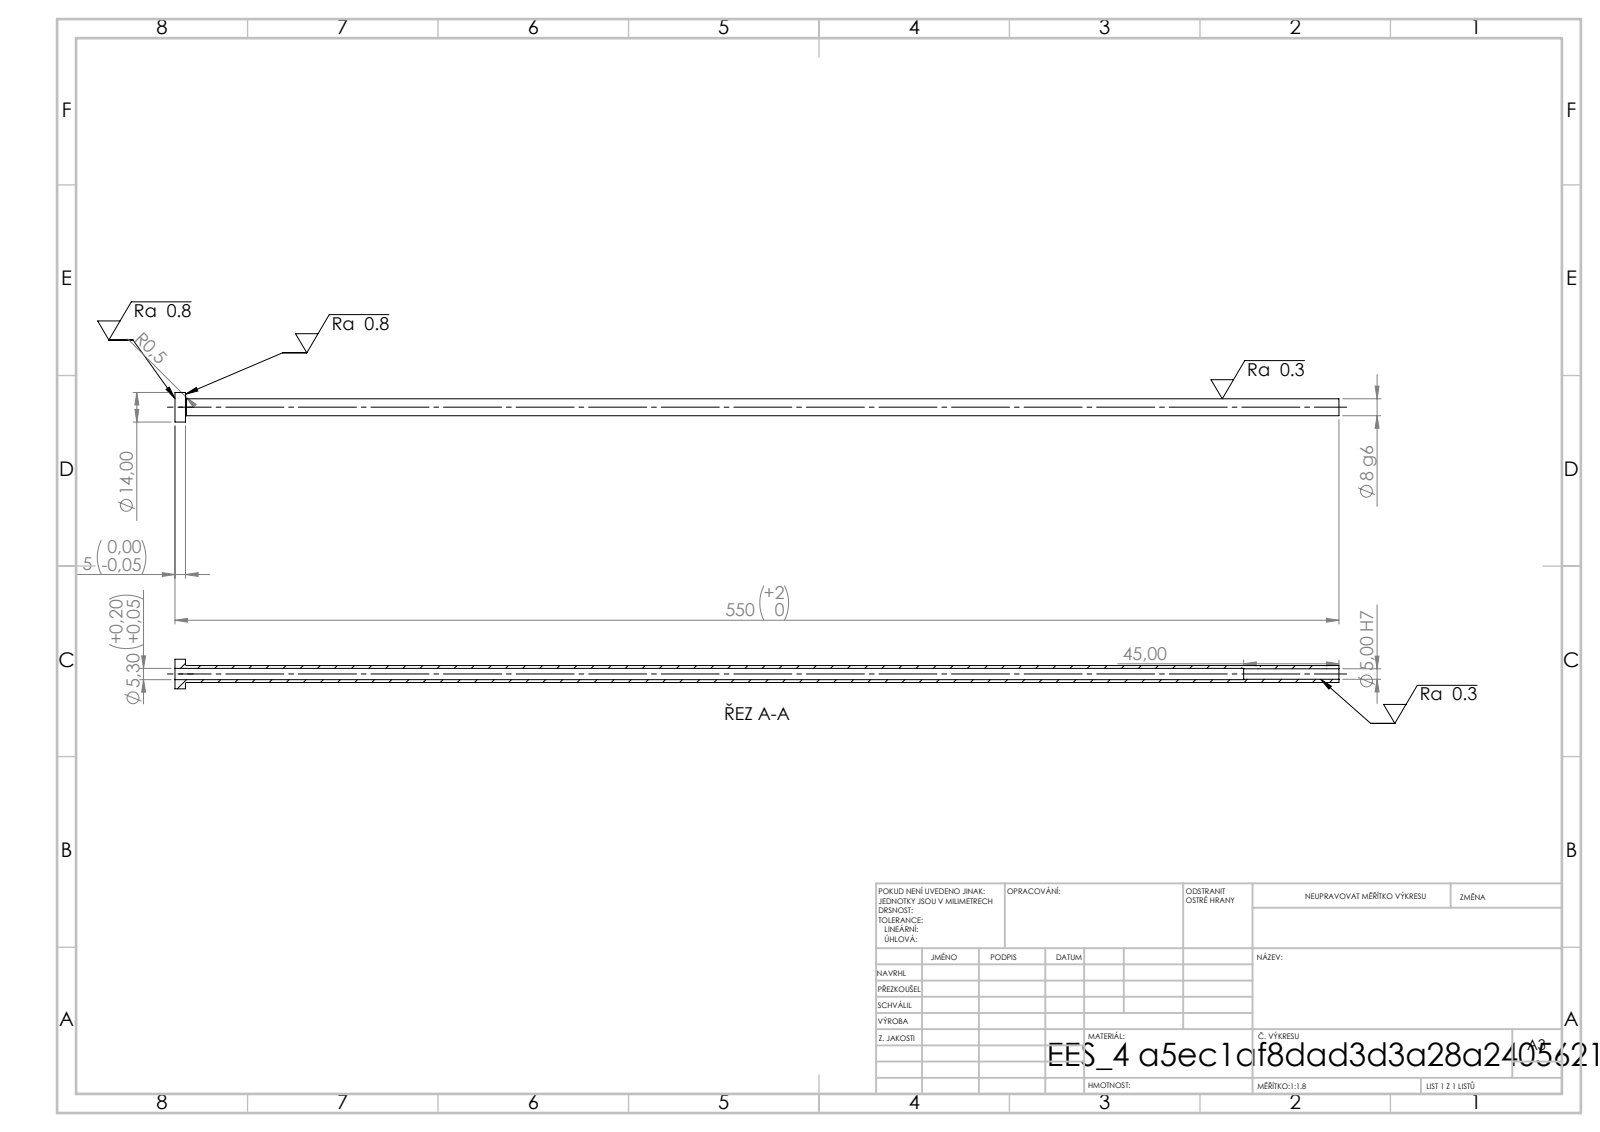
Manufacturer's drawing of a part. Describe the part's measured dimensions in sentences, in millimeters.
Its 3-D file was written by "SolidWorks 2019 (CONFIG_CONTROL_DESIGN)". It is 1 solid with 14 faces: 4 planar, 8 cylindrical and 2 other. Overall it measures 550 by 14 by 14 millimeters. Its volume is 16 141 cubic millimeters and its surface area 23 296 square millimeters. Round holes: 1 of diameter 5, 1 of diameter 5.3. Round bosses or shafts: 1 of diameter 14, 1 of diameter 8. The main face-to-face distances are 5, 550, 545, 505, 500, 45.
